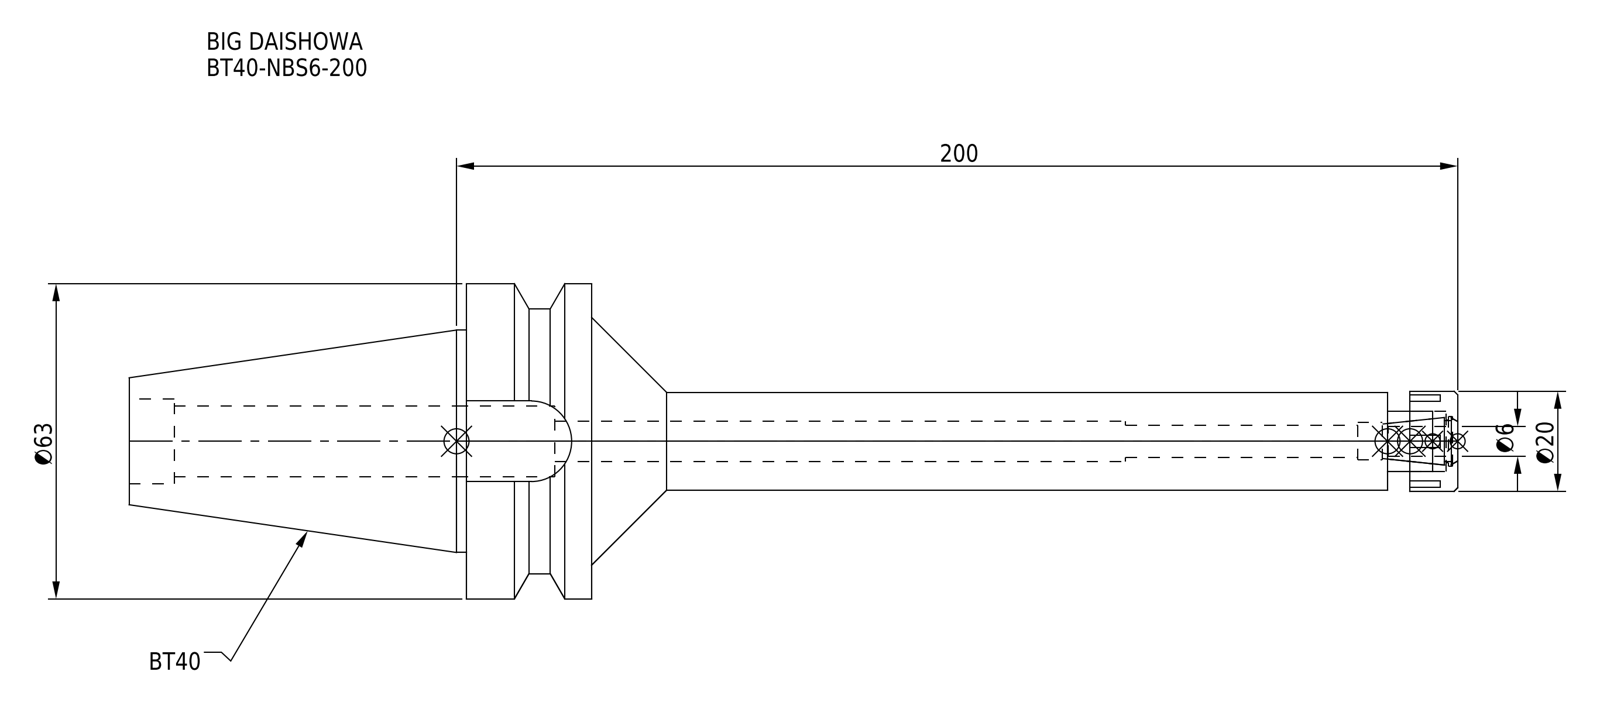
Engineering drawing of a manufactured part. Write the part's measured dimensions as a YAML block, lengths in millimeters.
part_name: "DXF_TEMP_ASSY_ASM_4_ASM.stp; BT40-NBS6-200; NBN6_1.stp; BT40-NBS6-200.stp (+3 more)"
step_written_by: "SolidWorks 2019 (CONFIG_CONTROL_DESIGN)"
units: millimeters
bodies: {solids: 2, faces: 93, planar: 45, cylindrical: 34, other: 14}
overall_size: [265.4, 63, 63]
volume: 173075
surface_area: 38089
round_holes:
  - {diameter: 6.4, count: 1}
  - {diameter: 7.5, count: 1}
  - {diameter: 8, count: 1}
  - {diameter: 8.5, count: 1}
  - {diameter: 10, count: 1}
  - {diameter: 12, count: 1}
  - {diameter: 14.2, count: 1}
  - {diameter: 17, count: 1}
round_bosses_or_shafts:
  - {diameter: 63, count: 1}
  - {diameter: 53, count: 1}
  - {diameter: 44.45, count: 1}
  - {diameter: 20, count: 1}
  - {diameter: 19.5, count: 1}
partial_cylinders:
  - {radius: 8.05, count: 1}
face_to_face_distances: [25, 45, 92.4, 67.4, 251.4, 4.5, 173, 198, 265.4, 14]
